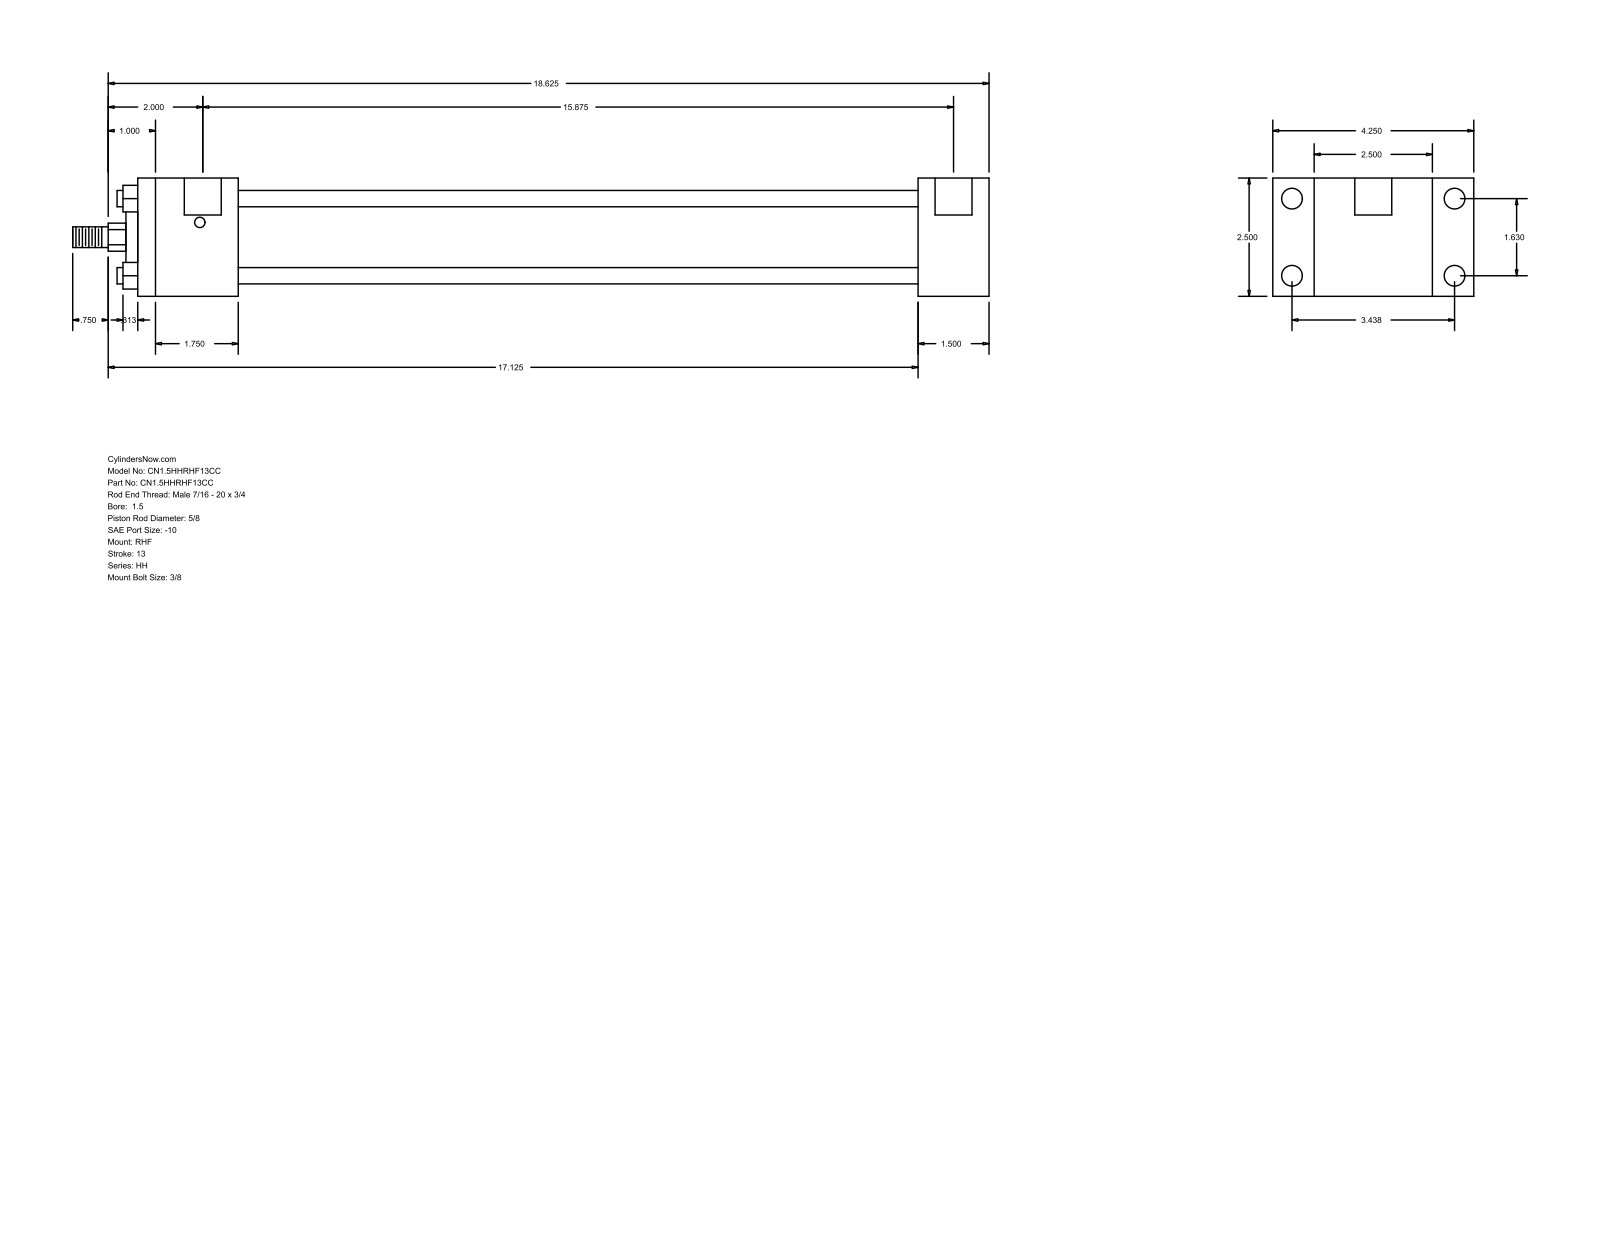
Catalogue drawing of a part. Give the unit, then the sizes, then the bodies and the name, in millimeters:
Units: millimetres
Overall size (bounding box): 492.12 × 107.95 × 63.5
Round holes (diameter × count): ⌀5.56 ×4, ⌀11.13 ×4, ⌀19.84 ×2
Round bosses / shafts (diameter × count): ⌀8.76 ×4, ⌀44.45 ×1, ⌀28.57 ×1, ⌀15.88 ×1, ⌀11.11 ×1
Partial cylindrical surfaces — rounded edges, fillets, slot ends (radius × count): R7.54 ×1
Main face-to-face distances: 63.5, 22.23, 85.73, 38.09, 419.1, 457.19, 107.96, 53.97, 365.13, 403.22
Hole centre spacings: 1.59, 41.4, 87.32, 96.64, 404.81, 406.4, 403.22
Bodies: 0 solids, 88 faces (60 planar, 28 cylindrical, 0 other)
Part name (STEP PRODUCT): HH_RHF__0150_0.625
STEP written by: GSSL Pune (CONFIG_CONTROL_DESIGN)
